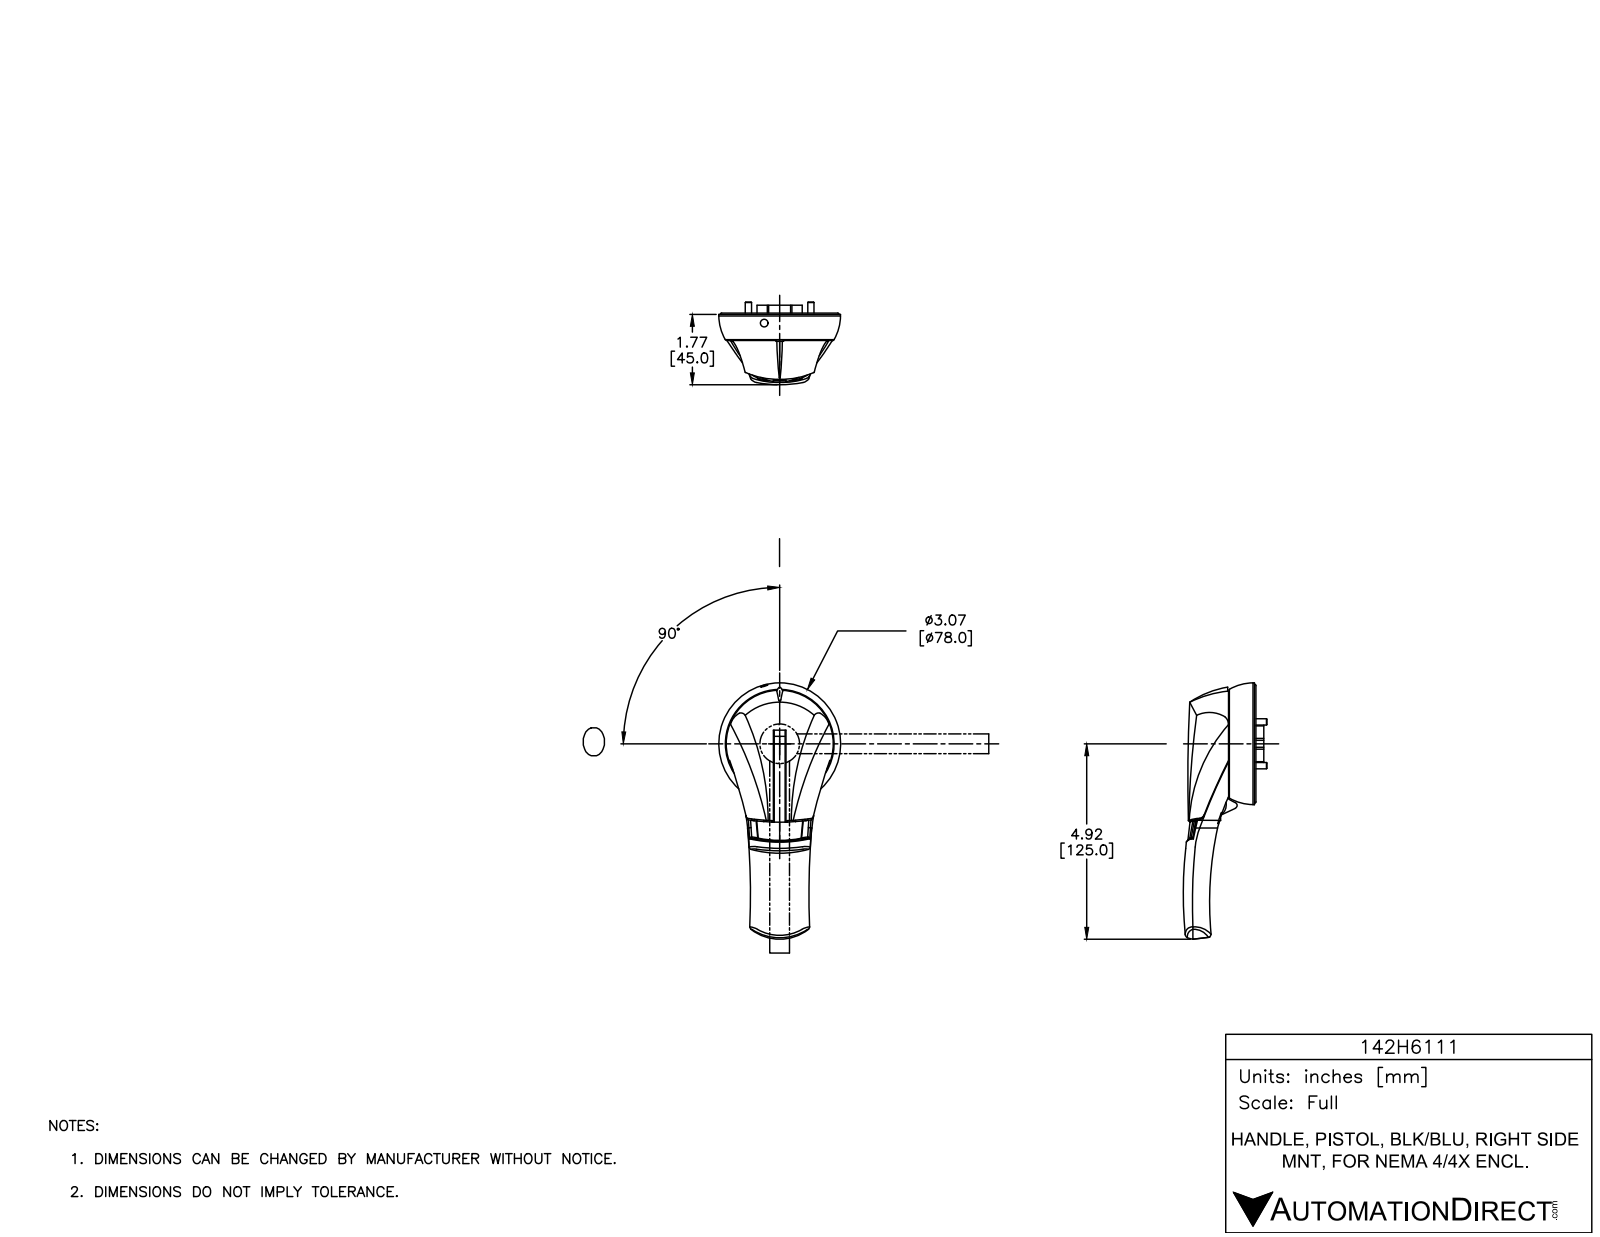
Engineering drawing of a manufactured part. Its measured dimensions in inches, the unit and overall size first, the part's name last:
Units: inches
Overall size (bounding box): 6.458 × 3.07 × 2.079
Round holes (diameter × count): ⌀0.157 ×6, ⌀0.339 ×4, ⌀0.425 ×4, ⌀0.03 ×3, ⌀0.169 ×2, ⌀0.362 ×2, ⌀0.118 ×1, ⌀0.189 ×1, ⌀2.992 ×1
Round bosses / shafts (diameter × count): ⌀0.02 ×11, ⌀0.335 ×4, ⌀0.315 ×4, ⌀0.089 ×3, ⌀0.069 ×3, ⌀0.228 ×2, ⌀2.819 ×1, ⌀2.701 ×1
Partial cylindrical surfaces — rounded edges, fillets, slot ends (radius × count): R0.01 ×221, R0.015 ×20, R0.034 ×20, R0.03 ×15, R0.039 ×4, R0.025 ×3, R5.437 ×3, R0.079 ×2
Main face-to-face distances: 0.024, 0.701, 0.713, 0.689, 0.035, 0.102, 0.276, 0.173, 0.244, 0.047
Hole centre spacings: 0.961, 0.309, 0.669, 1.098, 1.102, 1.203, 1.575, 1.881
Volume: 9.514 in³ · Surface area: 87.32 in²
Bodies: 8 solids, 1516 faces (810 planar, 548 cylindrical, 158 other)
Part name (STEP PRODUCT): 142H6111
STEP written by: SolidWorks 2015 (AUTOMOTIVE_DESIGN)
